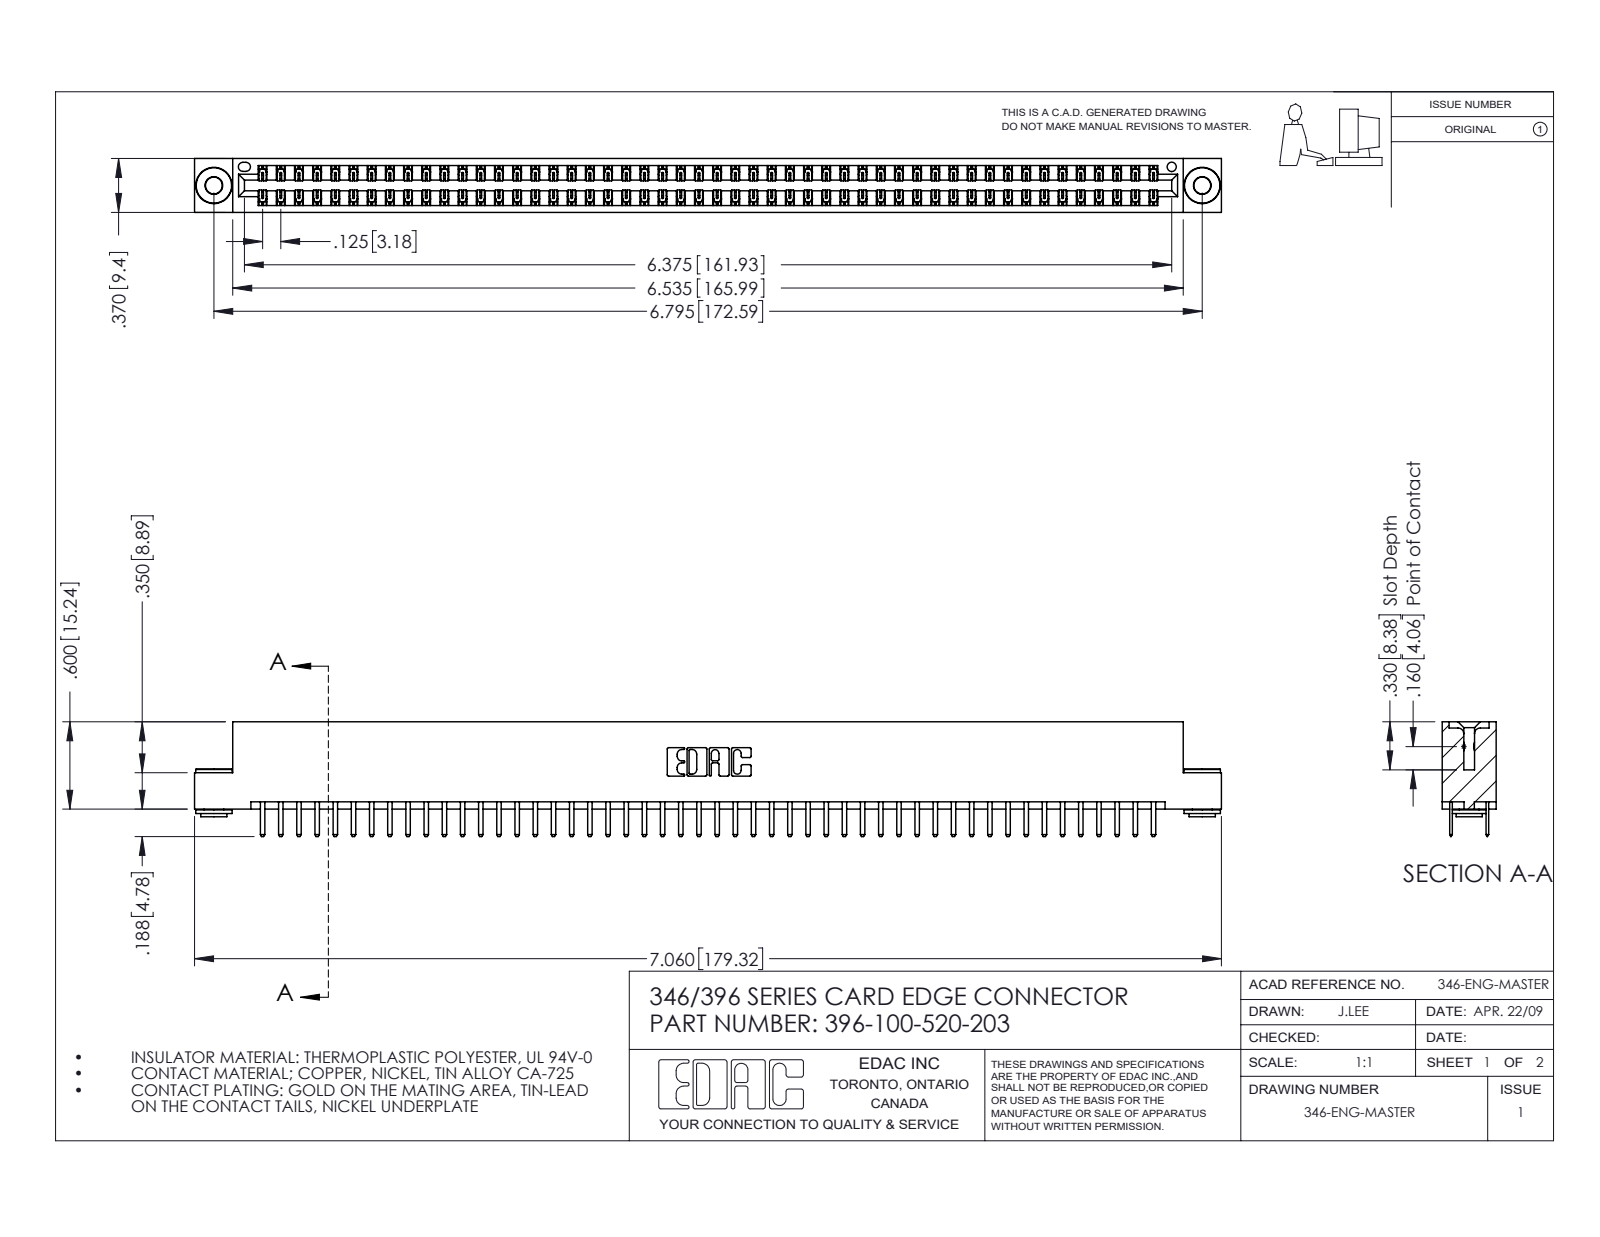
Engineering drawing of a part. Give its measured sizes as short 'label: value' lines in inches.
name: 345-250-002_345-250-002-102; 345-292-001_345-293-120; 346 Part_Flush Mounting Lugs - 0.156 Dia-TH; 396-100-520-203
written by: SolidWorks 2016 (CONFIG_CONTROL_DESIGN)
unit: in
bodies: 103 solids, 5760 faces (3786 planar, 1966 cylindrical, 8 other)
size: 7.06 × 0.788 × 0.37
volume: 1.069 in³; area: 37.7 in²
holes: 2× ⌀0.116, 2× ⌀0.156, 1× ⌀0.064
bosses: 2× ⌀0.25, 2× ⌀0.18, 2× ⌀0.136
rounds: 150× R0.006, 104× R0.01, 22× R0.01, 6× R0.007, 6× R0.031, 3× R0.026, 2× R0.014, 2× R0.022
face distances: 0.048, 0.322, 0.25, 0.37, 0.025, 0.275, 0.072, 0.298, 0.148, 0.222
hole spacings: 0.246, 6.586, 6.795
